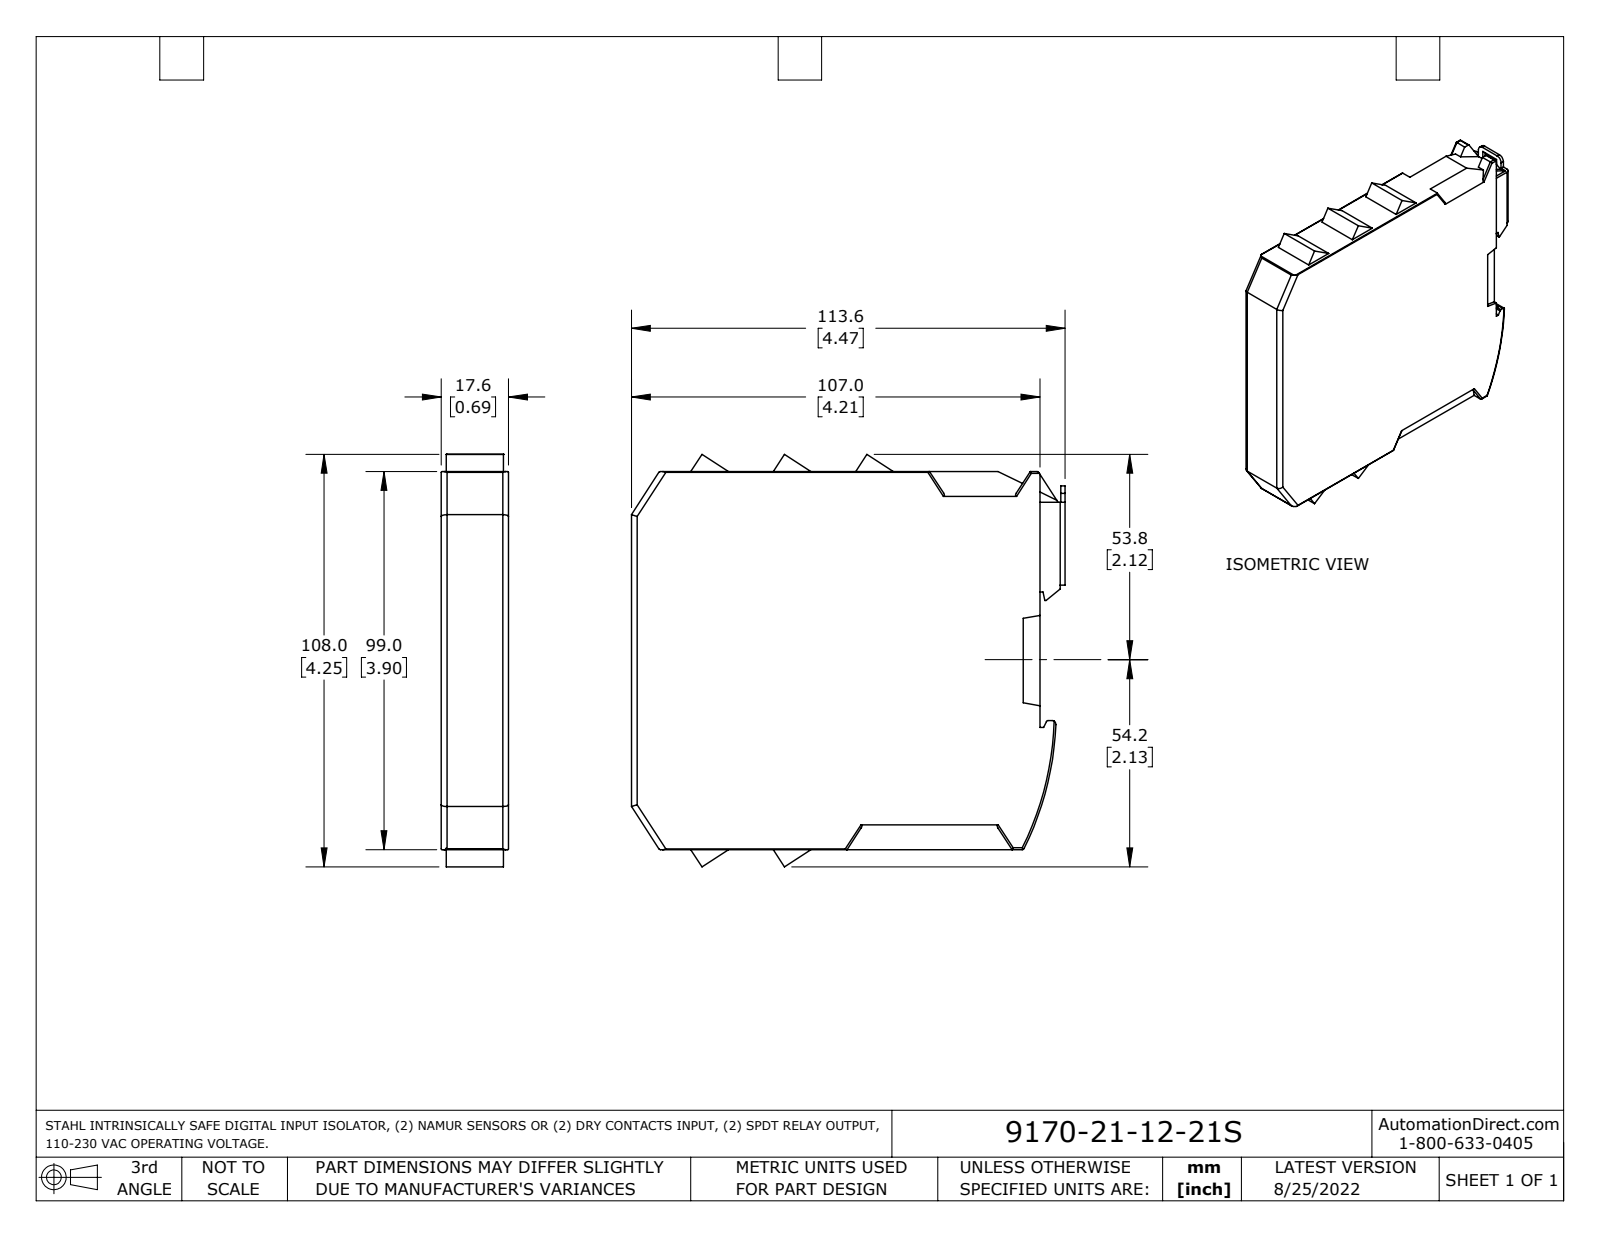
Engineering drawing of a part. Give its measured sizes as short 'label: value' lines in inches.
name: 9170-21-12-21S
written by: SolidWorks 2021 (AUTOMOTIVE_DESIGN)
unit: in
bodies: 2 solids, 181 faces (127 planar, 52 cylindrical, 2 other)
size: 4.472 × 4.252 × 0.693
volume: 11.44 in³; area: 46.75 in²
rounds: 17× R0.02, 6× R0.059, 4× R0.008, 4× R0.028, 2× R0.051, 2× R0.079, 1× R0.039, 1× R3.15
face distances: 0.693, 3.898, 4.213, 0.041, 0.652, 0.217, 4.429, 0.043, 0.26, 4.472
